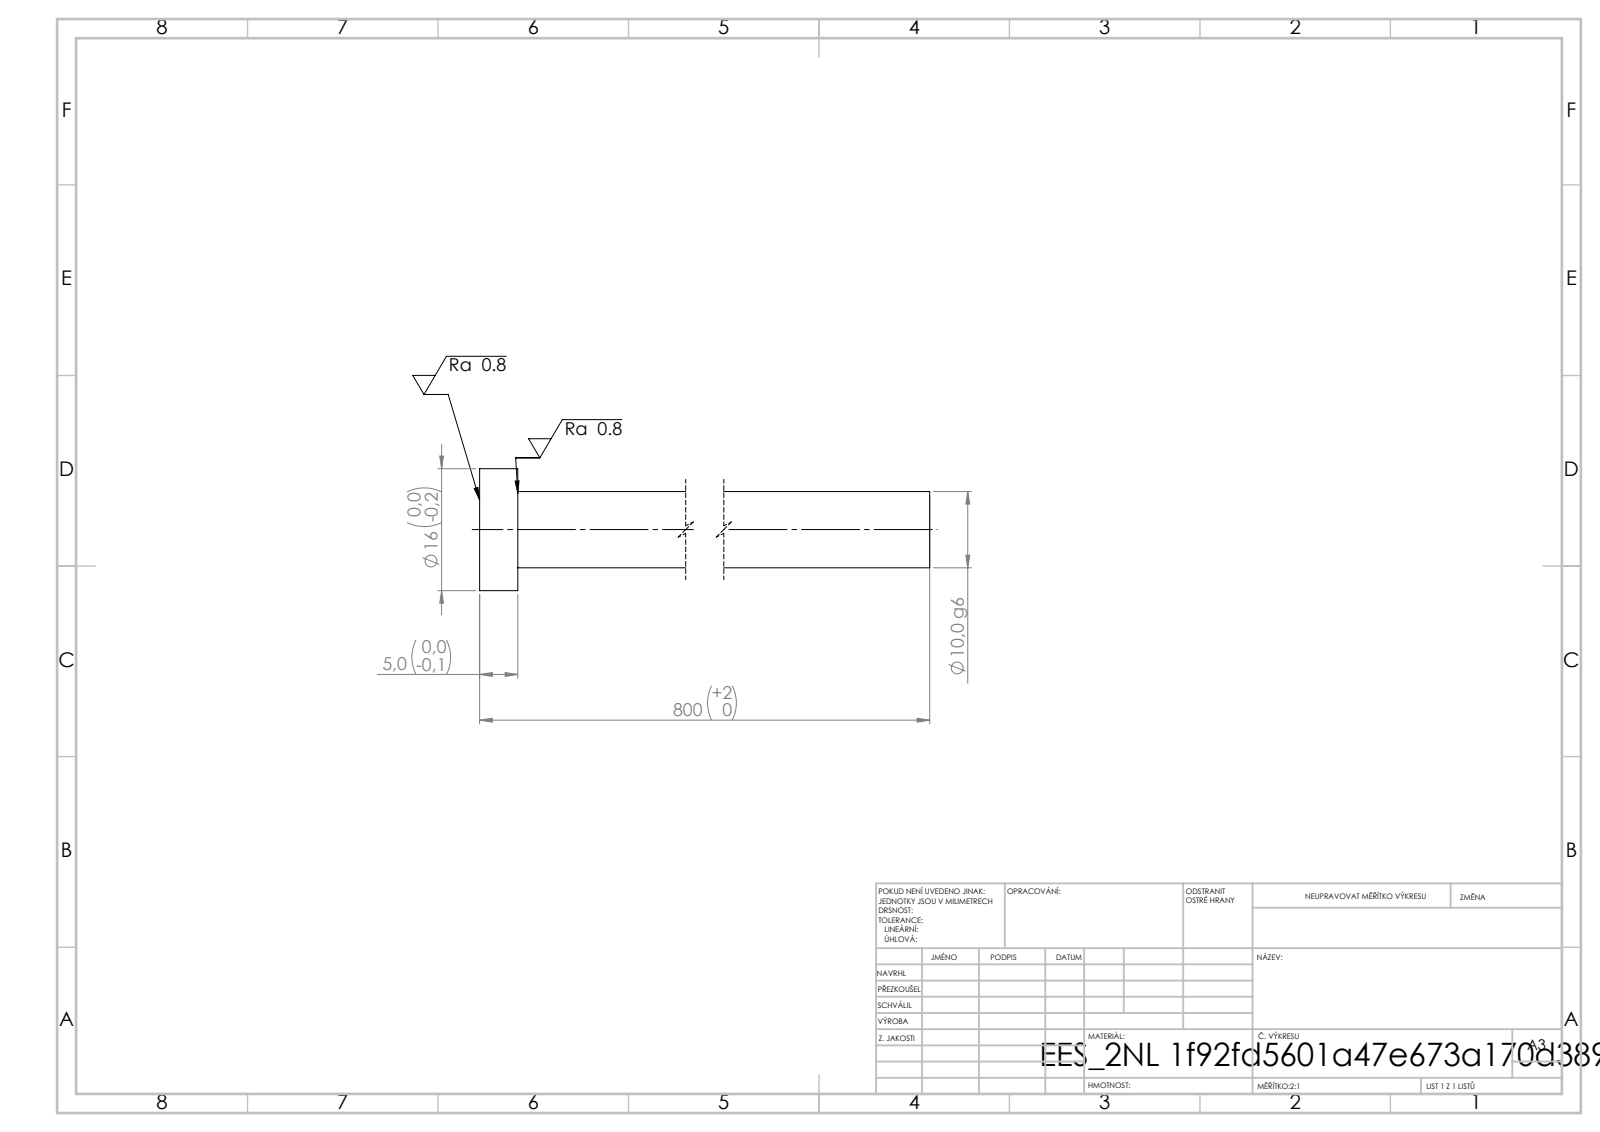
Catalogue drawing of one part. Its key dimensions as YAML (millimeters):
step_written_by: "SolidWorks 2019 (CONFIG_CONTROL_DESIGN)"
units: millimeters
bodies: {solids: 1, faces: 7, planar: 3, cylindrical: 4, other: 0}
overall_size: [800, 16, 16]
volume: 63444
surface_area: 25629
round_bosses_or_shafts:
  - {diameter: 16, count: 1}
  - {diameter: 10, count: 1}
face_to_face_distances: [5, 800, 795]
